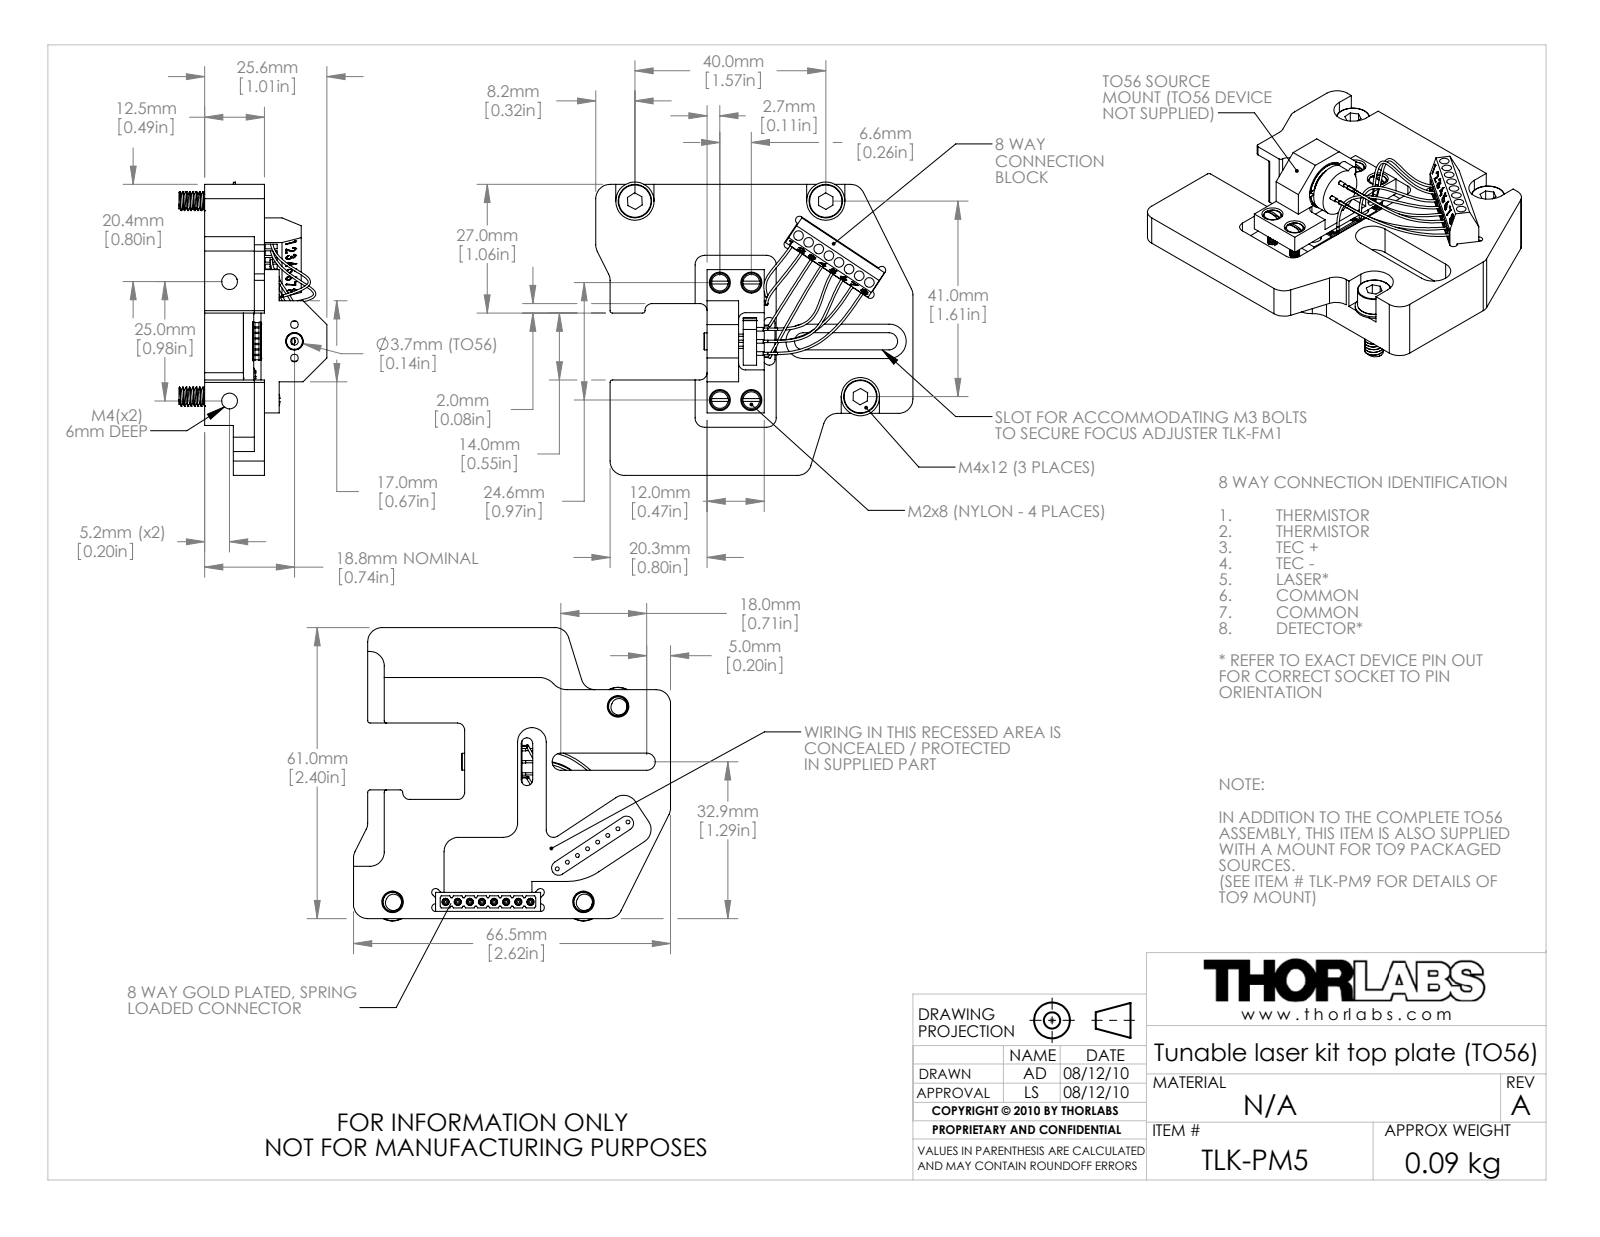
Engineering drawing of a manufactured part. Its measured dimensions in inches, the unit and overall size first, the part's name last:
Units: inches
Overall size (bounding box): 2.616 × 2.419 × 1.22
Round holes (diameter × count): ⌀0.079 ×8, ⌀0.173 ×4, ⌀0.063 ×3, ⌀0.146 ×3, ⌀0.177 ×3, ⌀0.13 ×2, ⌀0.098 ×1, ⌀0.156 ×1, ⌀0.409 ×1
Round bosses / shafts (diameter × count): ⌀0.02 ×14, ⌀0.059 ×8, ⌀0.031 ×7, ⌀0.008 ×6, ⌀0.079 ×4, ⌀0.058 ×4, ⌀0.03 ×4, ⌀0.276 ×3
Partial cylindrical surfaces — rounded edges, fillets, slot ends (radius × count): R0.118 ×16, R0.059 ×9, R0.031 ×8, R0.02 ×5, R0.157 ×5, R0.079 ×4, R0.051 ×2, R0.071 ×2
Main face-to-face distances: 0.492, 0.236, 0.256, 0.173, 0.083, 0.319, 0.142, 0.028, 0.098, 0.465
Hole centre spacings: 0.1, 0.2, 0.26, 0.3, 0.4, 0.5, 0.138, 0.21
Bodies: 0 solids, 981 faces (314 planar, 527 cylindrical, 140 other)
Part name (STEP PRODUCT): 21454-E0W
STEP written by: SolidWorks 2009 (AUTOMOTIVE_DESIGN)
